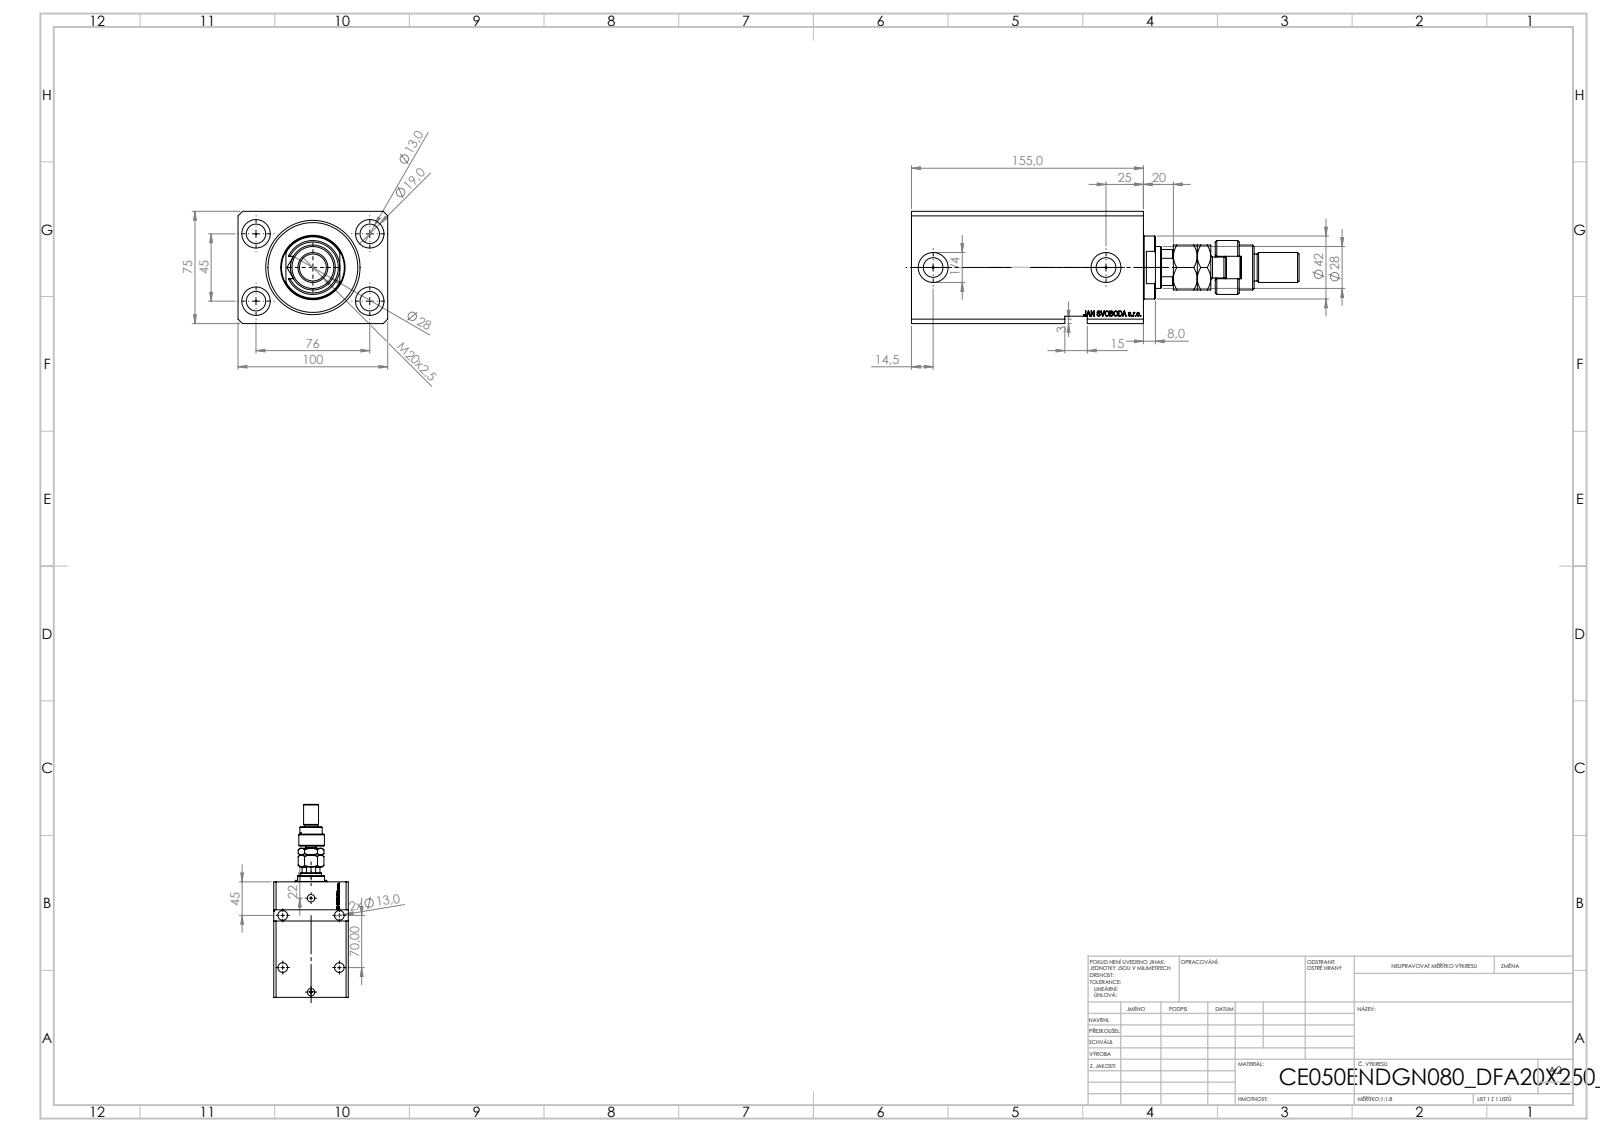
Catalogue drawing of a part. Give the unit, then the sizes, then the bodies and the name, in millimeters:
Units: millimetres
Overall size (bounding box): 259 × 100 × 75
Round holes (diameter × count): ⌀13 ×8, ⌀1.25 ×4, ⌀19 ×4, ⌀10 ×2, ⌀13.16 ×2, ⌀20 ×2, ⌀18.5 ×1, ⌀28 ×1, ⌀50 ×1, ⌀63 ×1
Round bosses / shafts (diameter × count): ⌀42 ×1, ⌀36 ×1, ⌀30 ×1, ⌀22 ×1, ⌀20 ×1, ⌀18 ×1, ⌀14 ×1
Partial cylindrical surfaces — rounded edges, fillets, slot ends (radius × count): R7.5 ×1, R12 ×1, R13.5 ×1
Main face-to-face distances: 75, 100, 20, 155, 11.9, 143.1, 135, 123.1, 30, 40
Hole centre spacings: 44.16, 76, 44.42, 45, 49.98, 50.33, 70, 88.32
Volume: 968 084 mm³ · Surface area: 175 545 mm²
Bodies: 5 solids, 1039 faces (491 planar, 129 cylindrical, 419 other)
Part name (STEP PRODUCT): FEMALE_PART_FOR_DFA; V250CE_E_Body; V250CE_C_VCP; V250CE_VC_E (+1 more)
STEP written by: SolidWorks 2019 (CONFIG_CONTROL_DESIGN)
